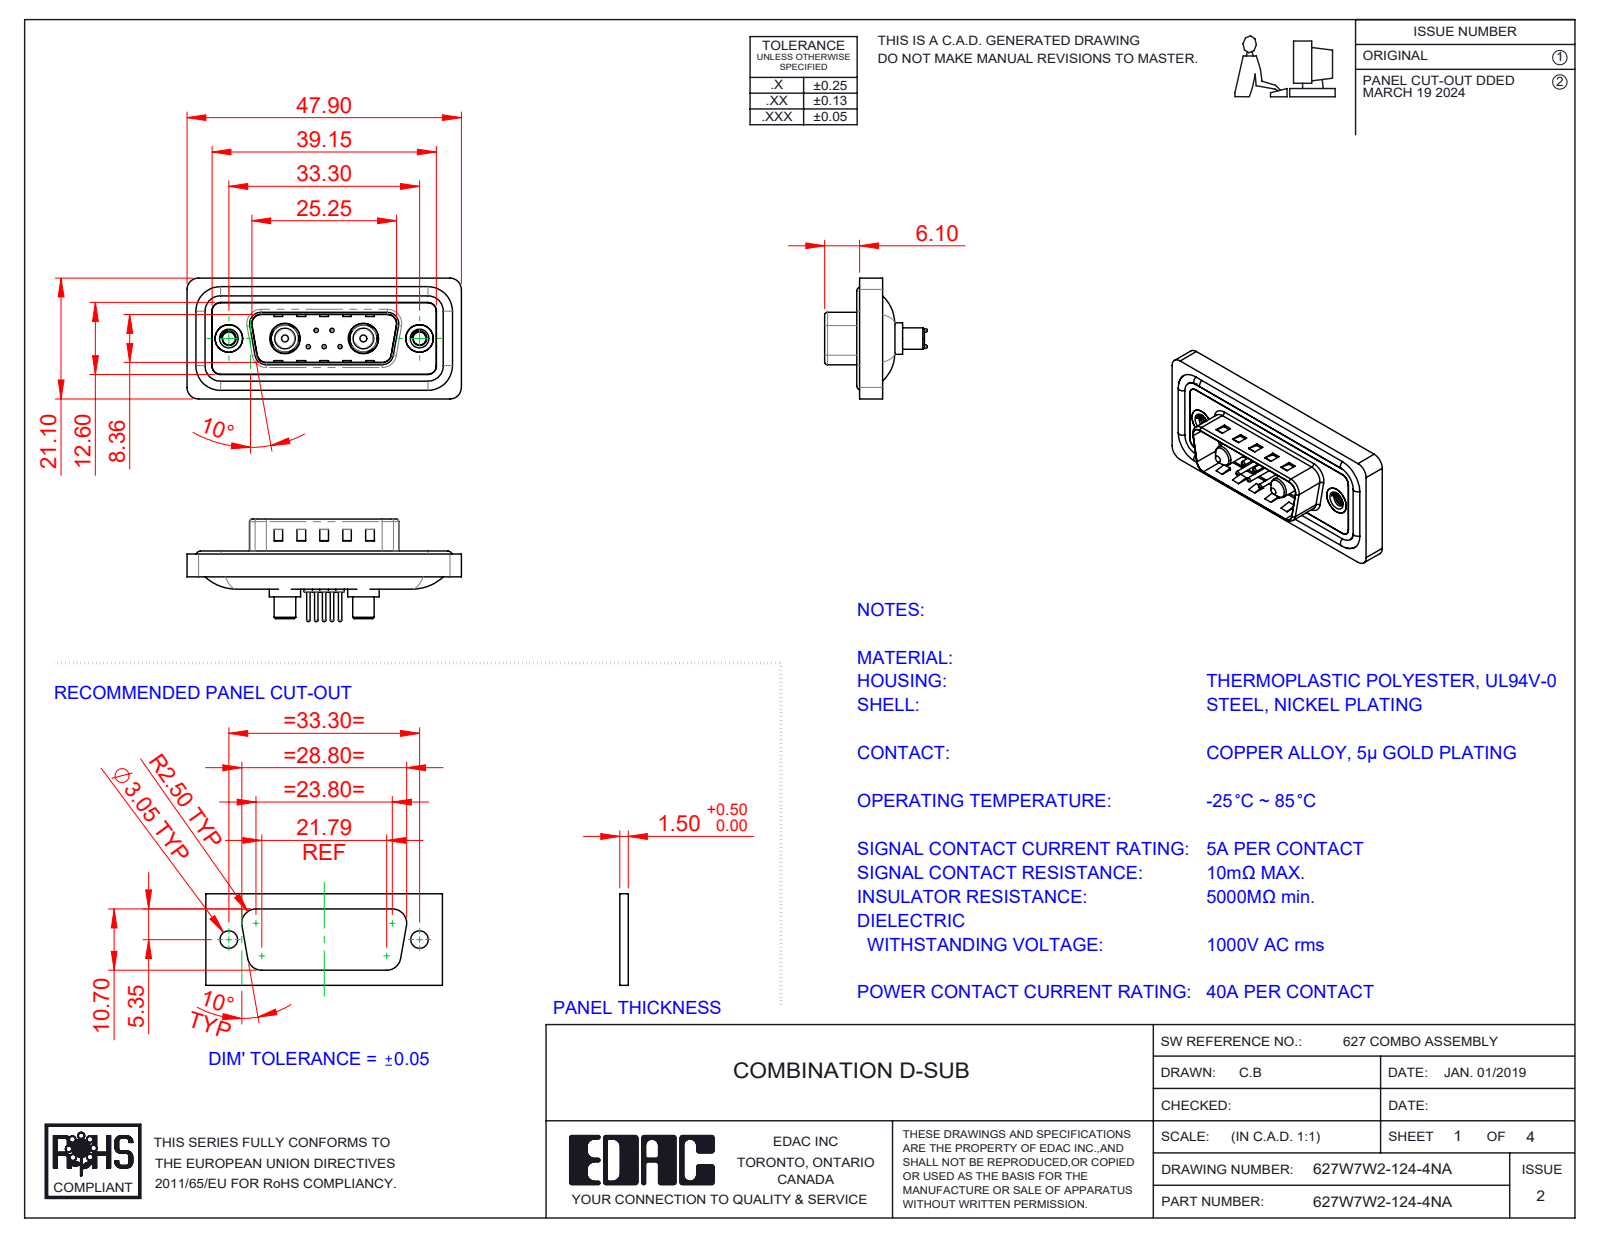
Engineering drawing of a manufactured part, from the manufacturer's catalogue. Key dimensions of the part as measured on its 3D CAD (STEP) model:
Part name (STEP PRODUCT): 627W7W2-124-4NA; 627Combo Contact Row 1_24; Power Pin_40A S; 627Combo Housing_7W2 (+5 more)
STEP written by: SolidWorks 2023 (CONFIG_CONTROL_DESIGN)
Units: millimetres
Bodies: 16 solids, 708 faces (232 planar, 294 cylindrical, 182 other)
Overall size (bounding box): 47.9 × 21.1 × 17.9
Volume: 5 555 mm³ · Surface area: 8 812 mm²
Round holes (diameter × count): ⌀0.75 ×5, ⌀1.6 ×5, ⌀2 ×5, ⌀2.26 ×2, ⌀4 ×2, ⌀4.8 ×2, ⌀4.85 ×2, ⌀5 ×2, ⌀5.3 ×2
Round bosses / shafts (diameter × count): ⌀1.5 ×5, ⌀0.6 ×5, ⌀1.6 ×4, ⌀5.5 ×2, ⌀5.2 ×2, ⌀4.9 ×2, ⌀4.75 ×2, ⌀3.75 ×2
Partial cylindrical surfaces — rounded edges, fillets, slot ends (radius × count): R1.5 ×26, R2 ×20, R0.5 ×8, R1.6 ×8, R0.25 ×4, R0.6 ×4, R0.65 ×4, R0.9 ×4
Main face-to-face distances: 0.4, 1.1, 1.6, 1.5, 0.5, 3.1, 2.9, 0.82, 9.58, 2.5
Hole centre spacings: 3.16, 2.77, 9.8, 23.5, 4.31, 4.33, 5.03, 5.04
